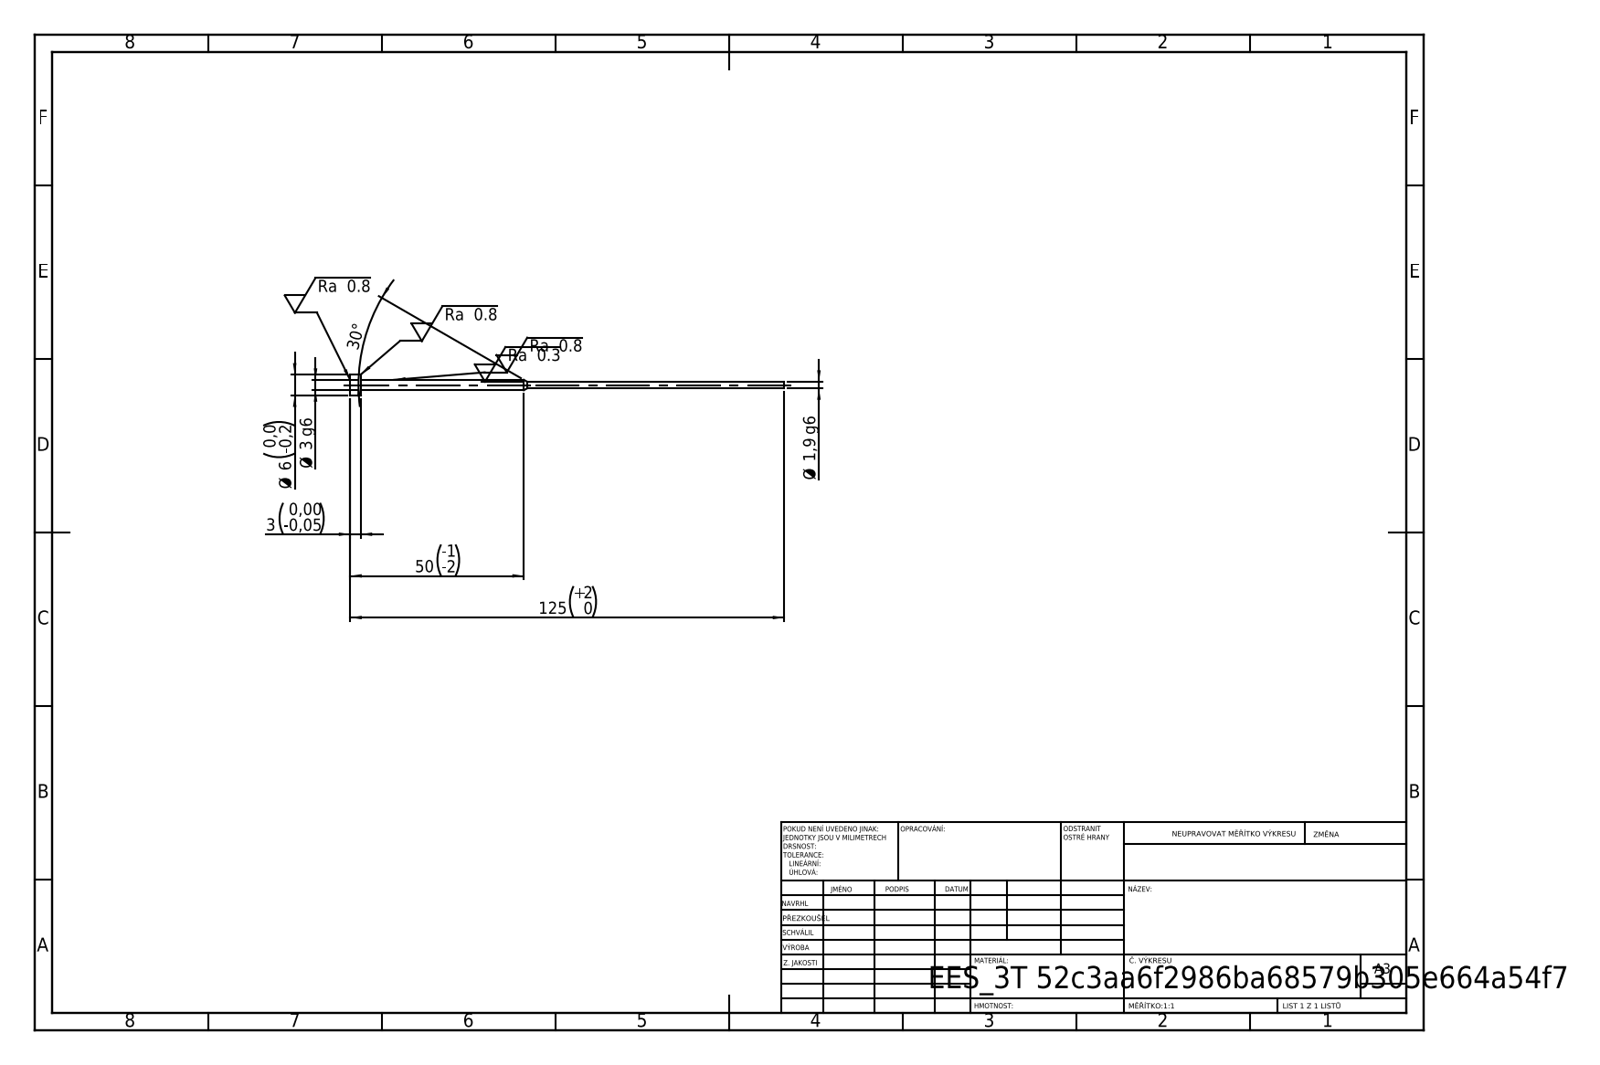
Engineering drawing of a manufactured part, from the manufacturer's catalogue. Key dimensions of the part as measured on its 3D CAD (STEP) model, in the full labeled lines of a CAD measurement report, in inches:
STEP written by: SolidWorks 2019 (CONFIG_CONTROL_DESIGN)
Units: inches
Bodies: 1 solid, 11 faces (3 planar, 6 cylindrical, 2 other)
Overall size (bounding box): 4.921 × 0.236 × 0.236
Volume: 0.039 in³ · Surface area: 1.553 in²
Round bosses / shafts (diameter × count): ⌀0.236 ×1, ⌀0.118 ×1, ⌀0.075 ×1
Main face-to-face distances: 0.118, 4.803, 4.921
